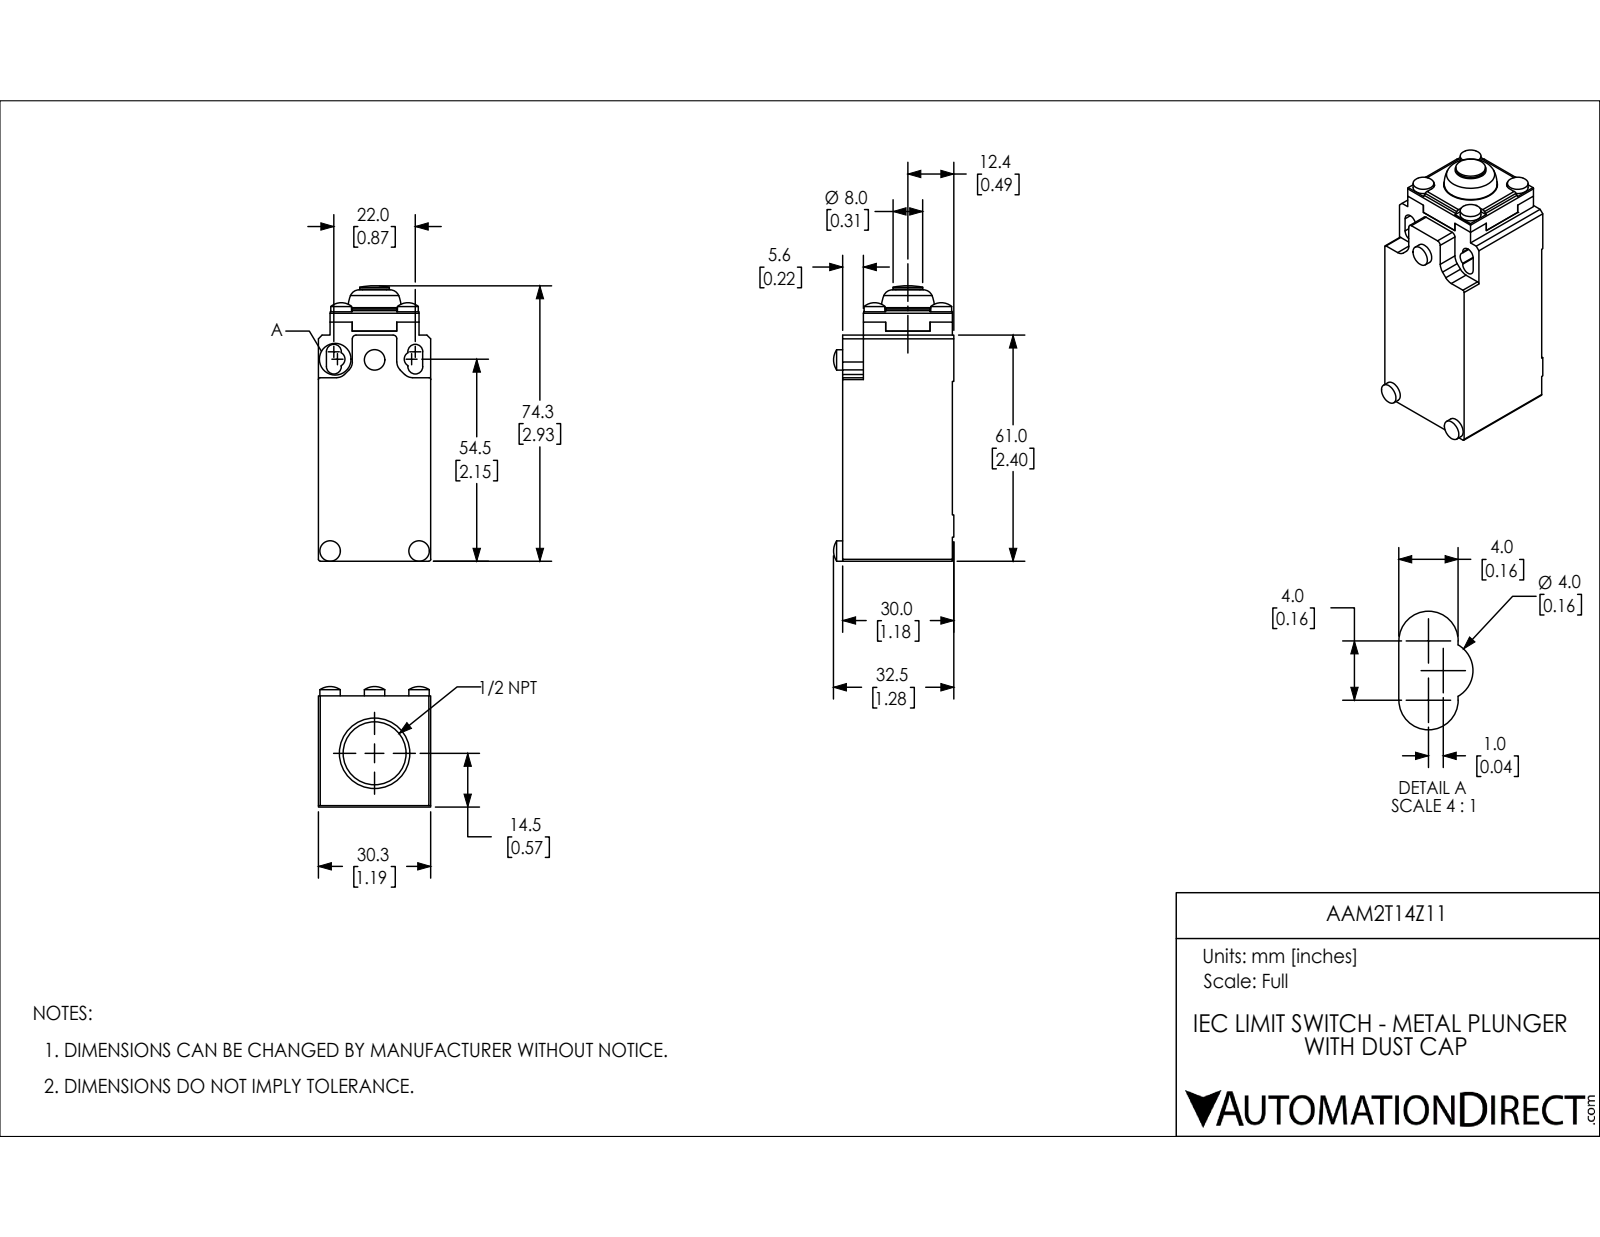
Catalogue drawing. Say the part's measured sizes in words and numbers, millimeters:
The part is named "AAM2T14Z11". Its 3-D file was written by "SolidWorks 2018 (AUTOMOTIVE_DESIGN)". It is 4 solids with 194 faces: 85 planar, 86 cylindrical and 23 other. Overall it measures 74.3 by 32.5 by 30.3 millimeters. Its volume is 56 160 cubic millimeters and its surface area 13 530 square millimeters. Round holes: 1 of diameter 8.1, 1 of diameter 14.5, 1 of diameter 17, 1 of diameter 19. Round bosses or shafts: 4 of diameter 5.6, 3 of diameter 5.5, 1 of diameter 14.3, 1 of diameter 8, 1 of diameter 6.5. Partial cylindrical surfaces (rounded edges, fillets, slot ends): 10 of radius 1, 8 of radius 3, 6 of radius 2, 4 of radius 0.5, 1 of radius 10, 1 of radius 10.2. The main face-to-face distances are 30.3, 29.6, 6, 0.4, 30, 62.1, 24, 1.1, 62.1, 6.2. The hole center spacings are 2.1.
